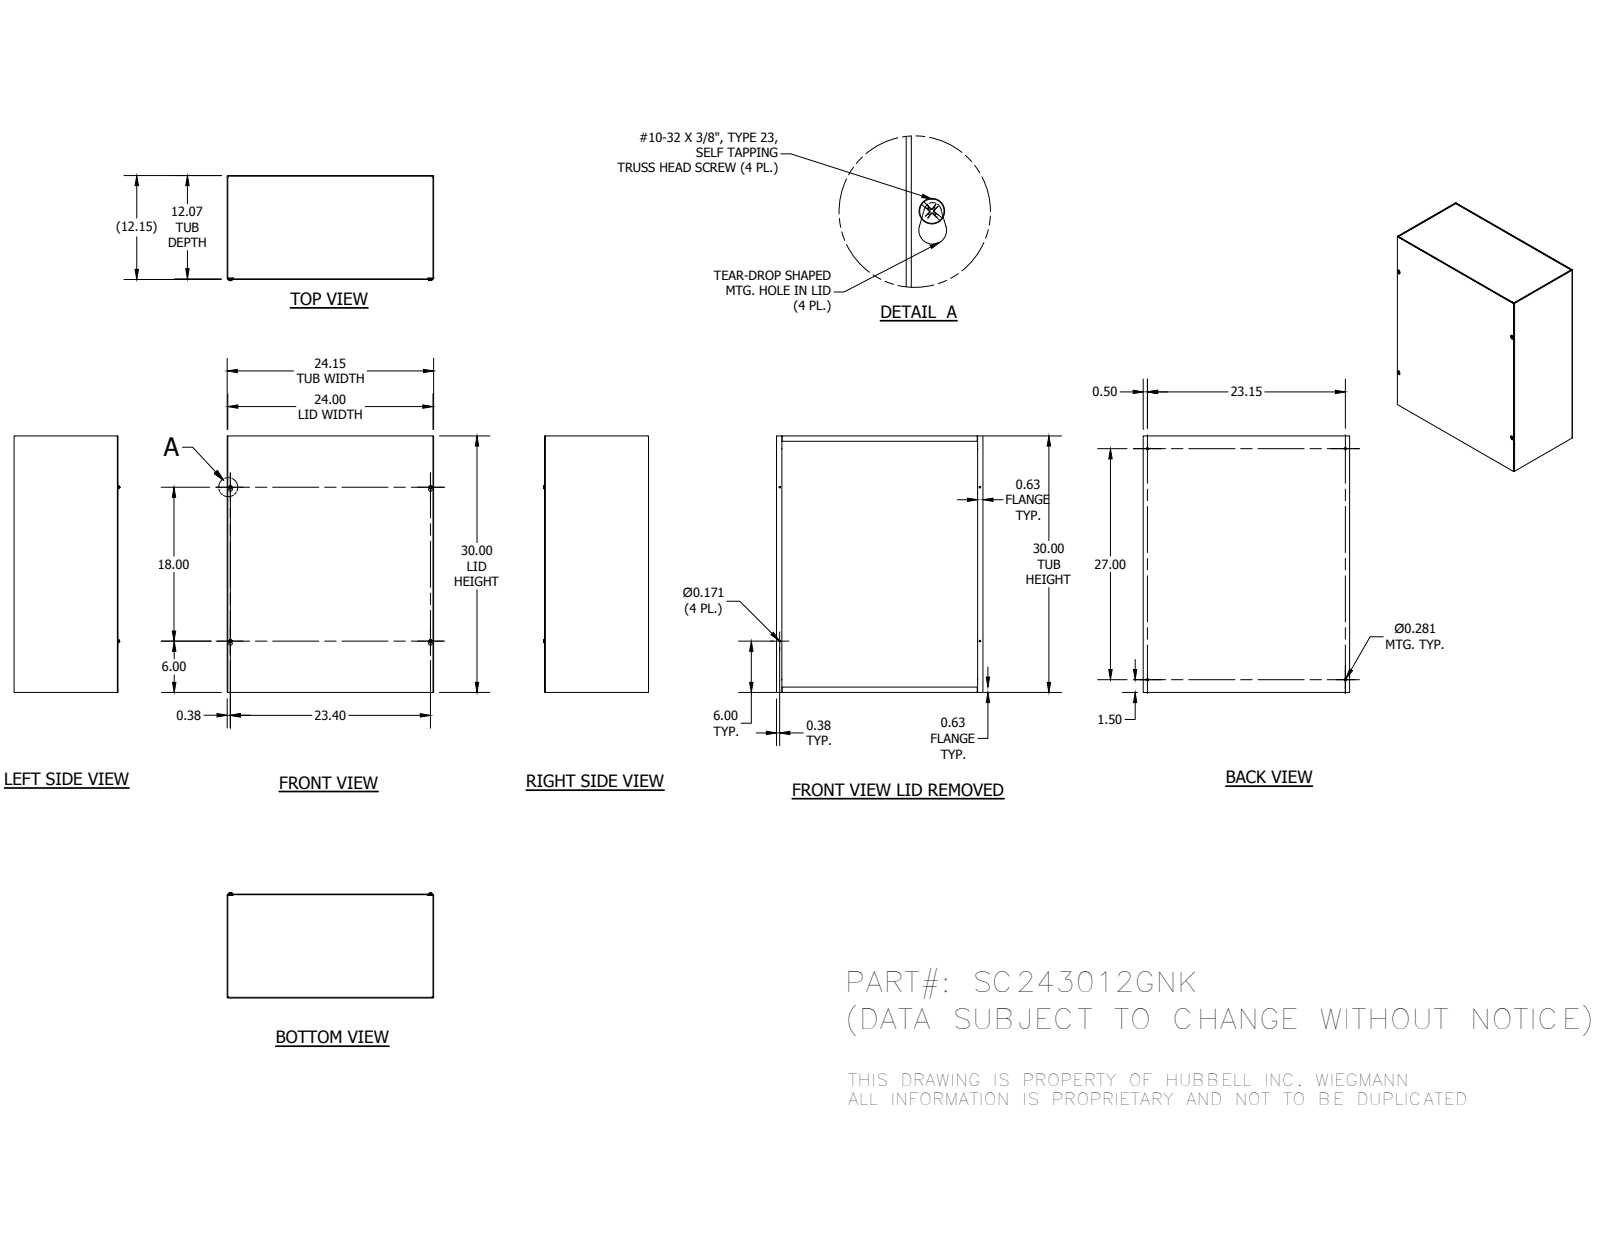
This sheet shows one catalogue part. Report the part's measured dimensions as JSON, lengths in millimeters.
{"part_name": "SC243012GNKBLR; SC2412GNKTB; SC2430GLPA; 37214 (+1 more)", "step_written_by": "Autodesk Inventor 2014 (AUTOMOTIVE_DESIGN)", "units": "millimeters", "bodies": {"solids": 8, "faces": 320, "planar": 192, "cylindrical": 44, "other": 84}, "overall_size": [762, 613.36, 311.91], "volume_mm3": 3450000, "surface_area_mm2": 3692000, "round_holes": [[4.34, 4], [7.14, 4]], "round_bosses_or_shafts": [[4.83, 4]], "partial_cylinders_radius": [[0.4, 12], [2.28, 12], [3.17, 4], [5.16, 4]], "face_to_face_distances": [1.88, 306.68, 304.8, 308.56, 611.48, 760.12, 609.6, 613.36, 762, 758.24], "hole_center_spacings": [114.34, 571.51, 602.08, 822.22, 457.2, 587.96, 594.3, 685.8]}
